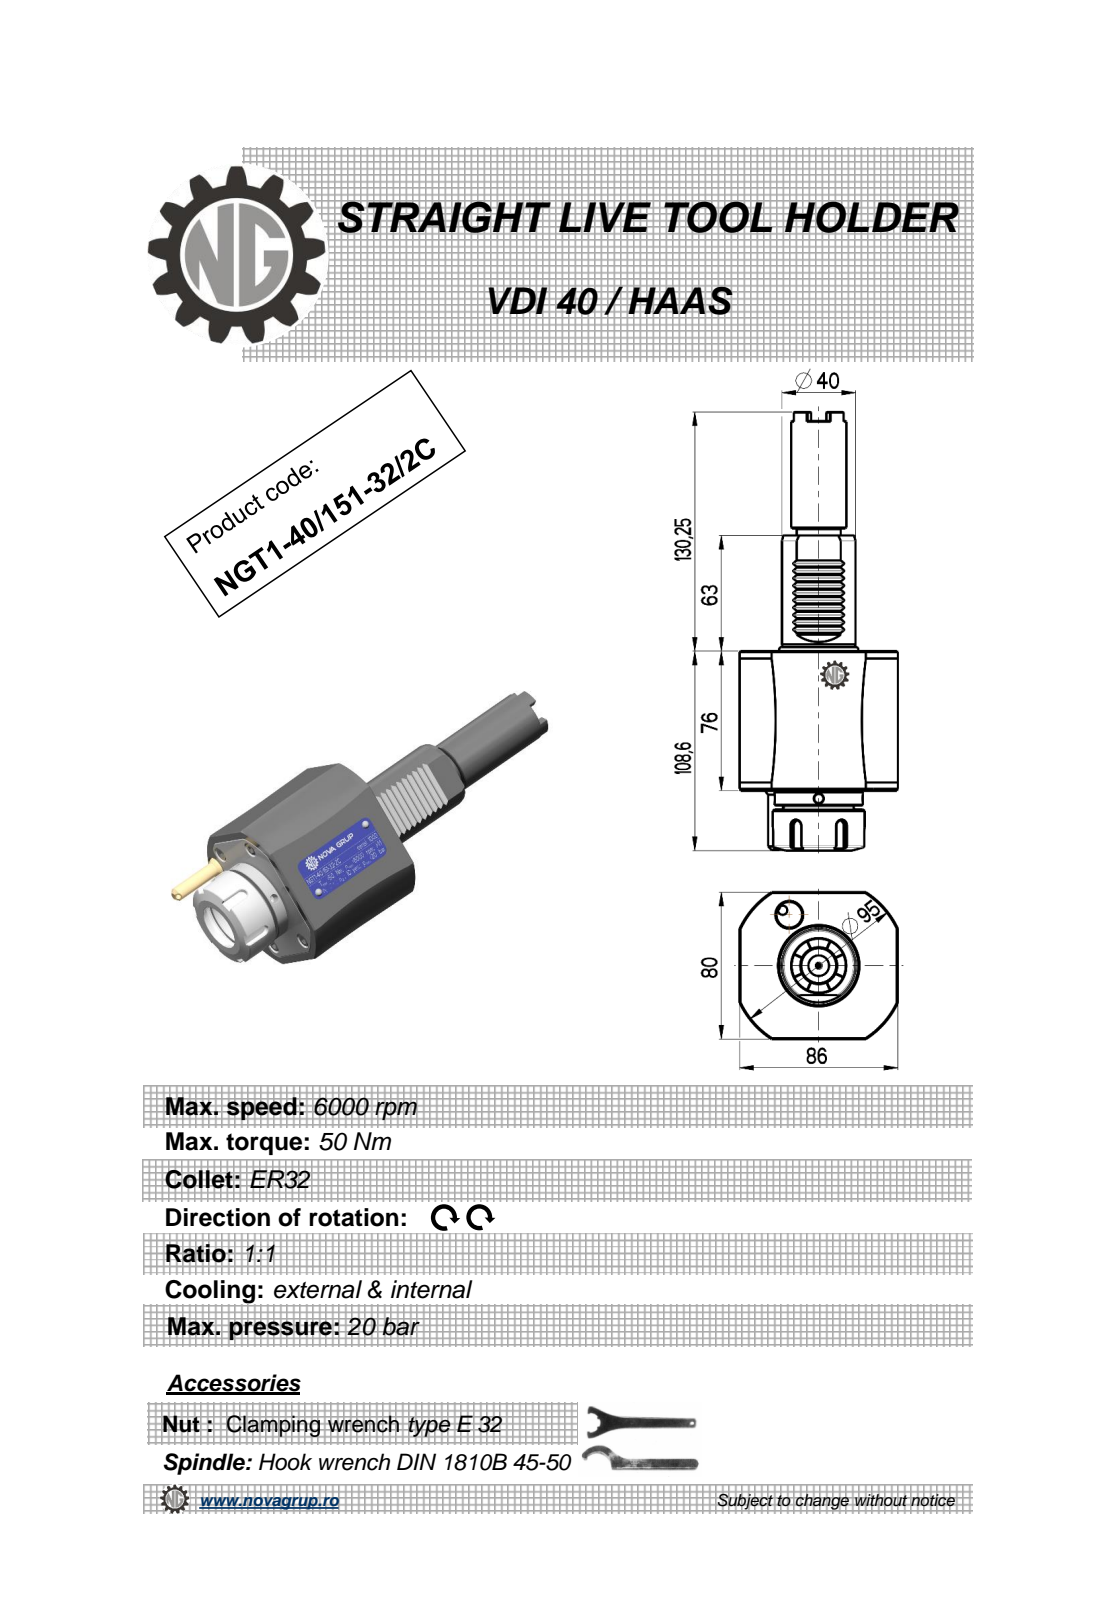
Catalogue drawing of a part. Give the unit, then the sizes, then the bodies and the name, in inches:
Units: inches
Overall size (bounding box): 9.404 × 3.386 × 3.213
Round holes (diameter × count): ⌀0.197 ×3, ⌀0.118 ×1, ⌀0.768 ×1, ⌀1.063 ×1
Round bosses / shafts (diameter × count): ⌀1.969 ×1, ⌀1.89 ×1, ⌀1.634 ×1, ⌀1.614 ×1, ⌀1.575 ×1, ⌀1.181 ×1, ⌀0.945 ×1, ⌀0.315 ×1
Partial cylindrical surfaces — rounded edges, fillets, slot ends (radius × count): R0.012 ×10, R0.009 ×6, R0.118 ×5, R1.87 ×1
Main face-to-face distances: 2.992, 3.15, 3.386, 0.111, 4.098, 1.106, 0.223, 2.48, 5.472, 6.579
Hole centre spacings: 1.575
Volume: 39.68 in³ · Surface area: 91.42 in²
Bodies: 1 solid, 306 faces (133 planar, 72 cylindrical, 101 other)
Part name (STEP PRODUCT): NGT1_40_151_32_1C
STEP written by: PRO/ENGINEER BY PARAMETRIC TECHNOLOGY CORPORATION, 2010280 (CONFIG_CONTROL_DESIGN)
